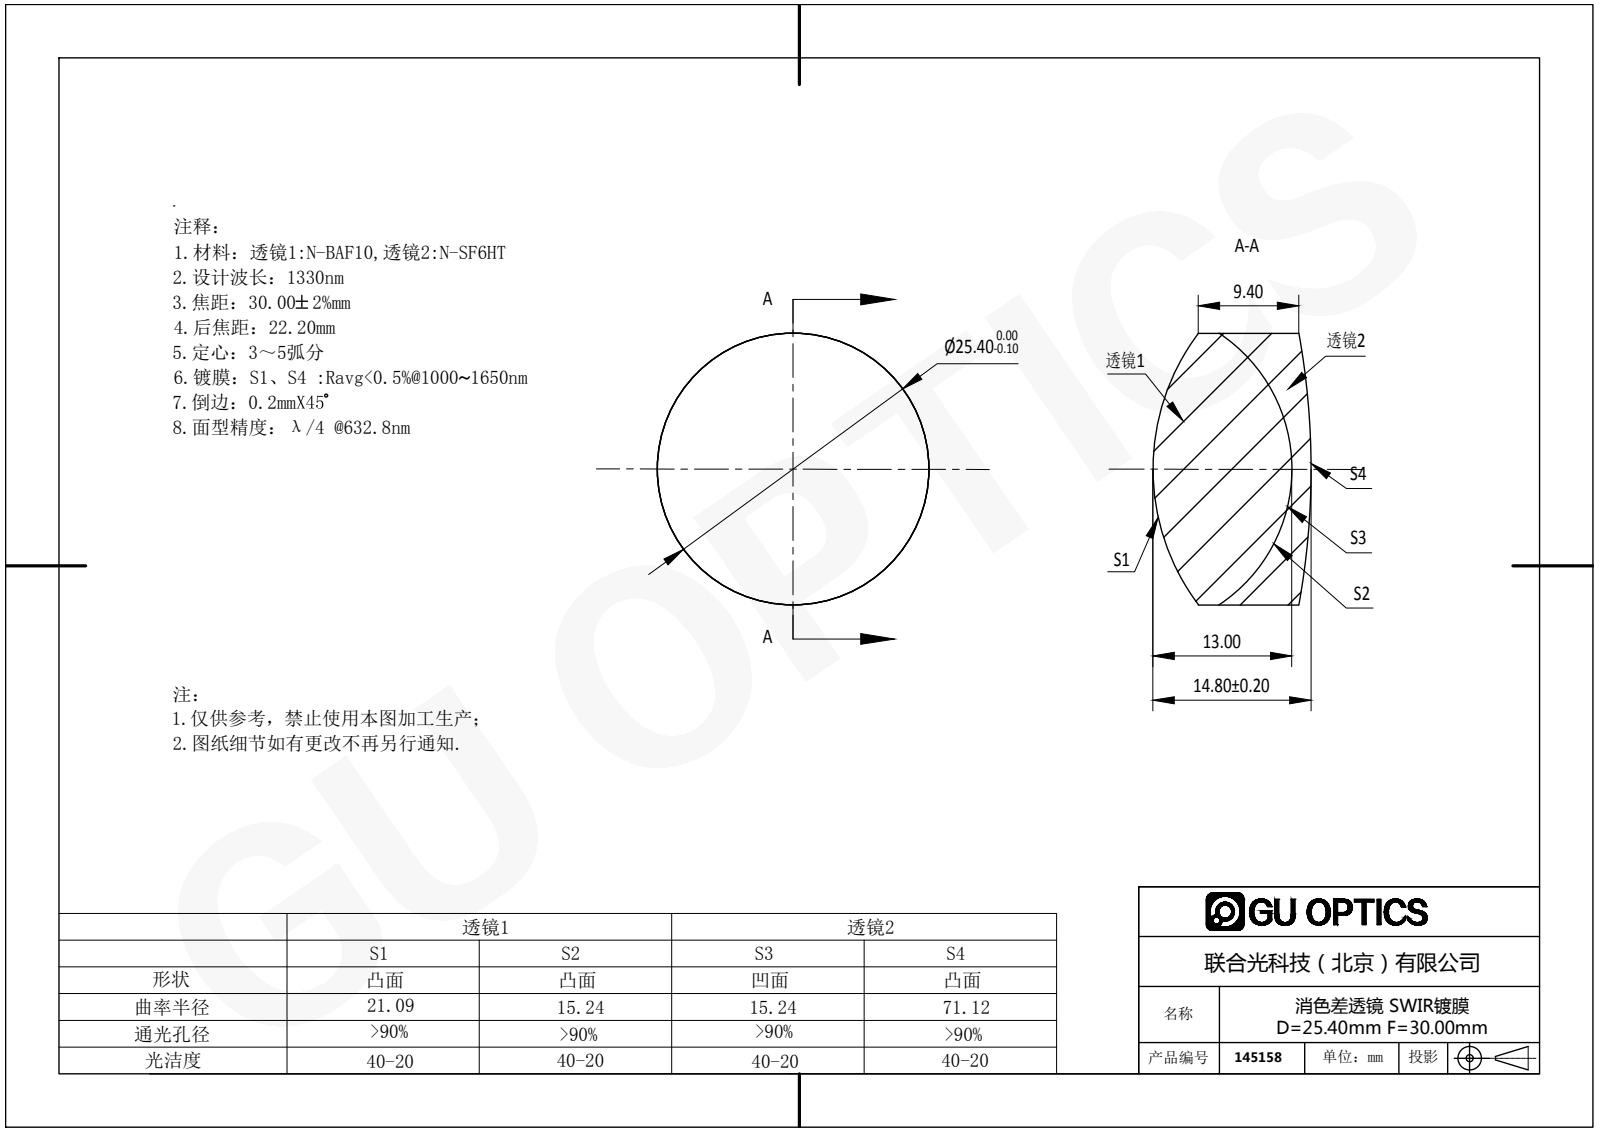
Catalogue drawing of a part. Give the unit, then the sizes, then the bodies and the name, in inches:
Units: inches
Overall size (bounding box): 1 × 1 × 0.583
Round bosses / shafts (diameter × count): ⌀1 ×1
Volume: 0.377 in³ · Surface area: 4.852 in²
Bodies: 2 solids, 12 faces (0 planar, 4 cylindrical, 8 other)
Part name (STEP PRODUCT): 145158
STEP written by: SolidWorks 2016 (AUTOMOTIVE_DESIGN)
